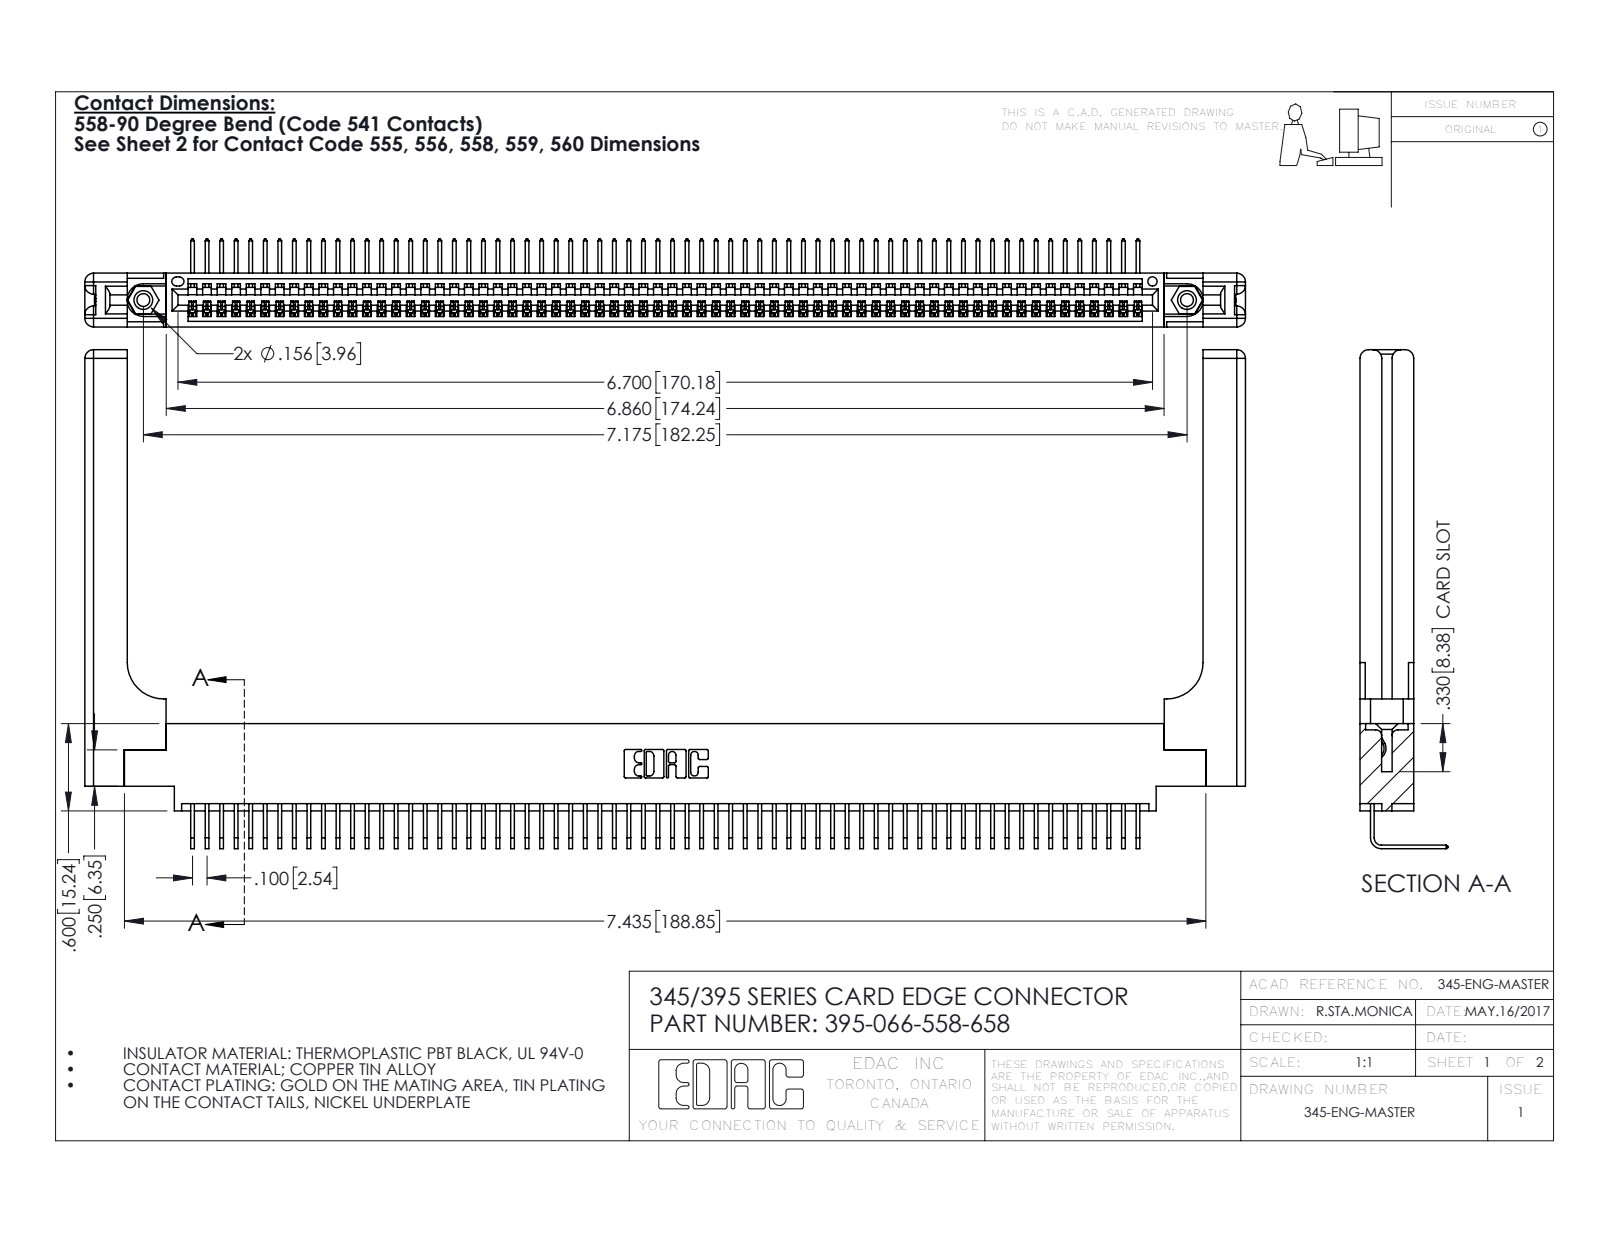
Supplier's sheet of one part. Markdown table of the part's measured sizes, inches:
| quantity | value |
| --- | --- |
| part name | 345-292-001_558 Tail - 2; 345-220-058_345-220-058; 345 Part_0.170 Offset - 0.156 Dia-TH; 395-066-558-658 (+1 more) |
| STEP written by | SolidWorks 2016 (CONFIG_CONTROL_DESIGN) |
| units | inches |
| bodies | 71 solids, 4346 faces (3004 planar, 1282 cylindrical, 60 other) |
| overall size | 7.979 × 3.429 × 0.605 |
| volume | 1.712 in³ |
| surface area | 51.2 in² |
| round holes (diameter × count) | 0.089 × 2, 0.125 × 2, 0.156 × 2, 0.064 × 1 |
| round bosses / shafts (diameter × count) | 0.155 × 2 |
| partial cylindrical surfaces (radius × count) | 0.006 × 132, 0.01 × 22, 0.06 × 16, 0.007 × 6, 0.031 × 6, 0.026 × 3, 0.03 × 2, 0.031 × 2 |
| main face-to-face distances | 0.072, 0.37, 0.298, 0.098, 0.272, 0.025, 0.2, 0.225, 0.148, 0.15 |
| hole center spacings | 0.27, 6.939, 7.175 |
